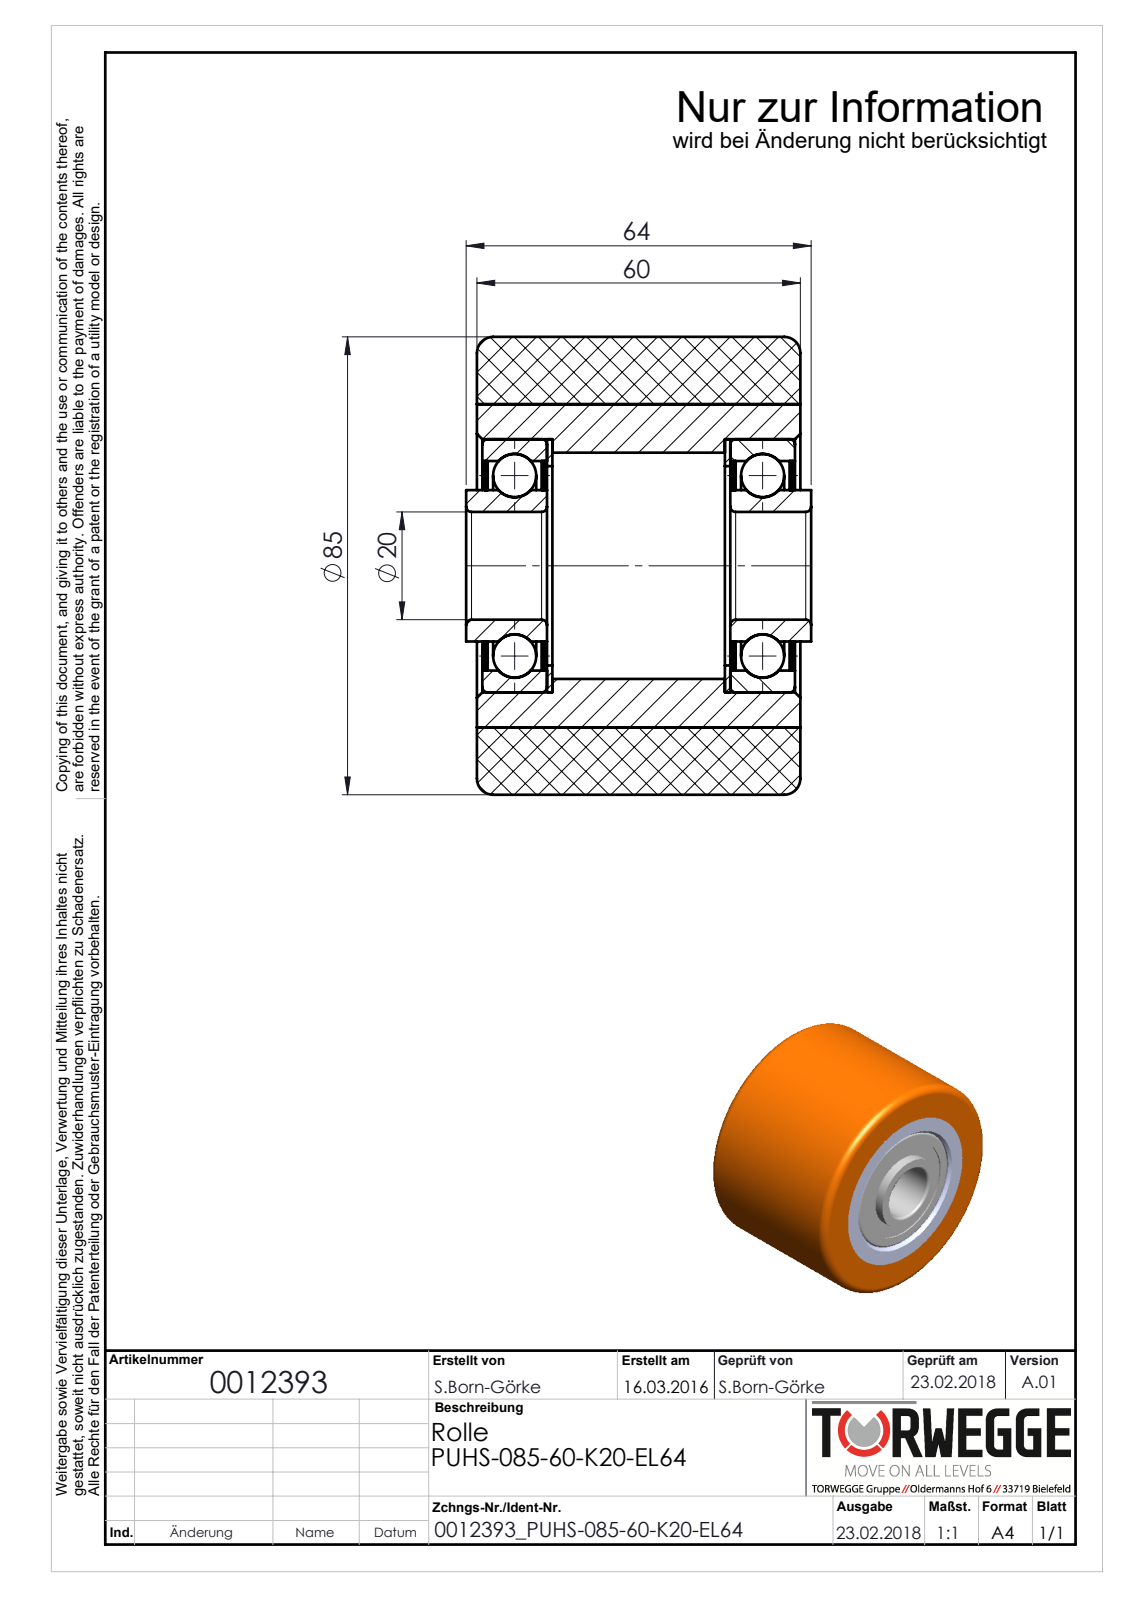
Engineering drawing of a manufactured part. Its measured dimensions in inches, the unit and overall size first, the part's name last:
Units: inches
Overall size (bounding box): 3.346 × 3.346 × 2.52
Round holes (diameter × count): ⌀0.787 ×1, ⌀1.531 ×1, ⌀1.654 ×1, ⌀1.85 ×1, ⌀2.362 ×1
Round bosses / shafts (diameter × count): ⌀3.346 ×1, ⌀1.106 ×1
Main face-to-face distances: 2.362, 0.059, 2.303, 0.039, 2.323, 0.02, 2.264, 2.244, 0.079, 0.118
Bodies: 0 solids, 56 faces (10 planar, 26 cylindrical, 20 other)
Part name (STEP PRODUCT): 0012393_PUHS-085-60-K20-EL64
STEP written by: SolidWorks 2016 (AUTOMOTIVE_DESIGN)
